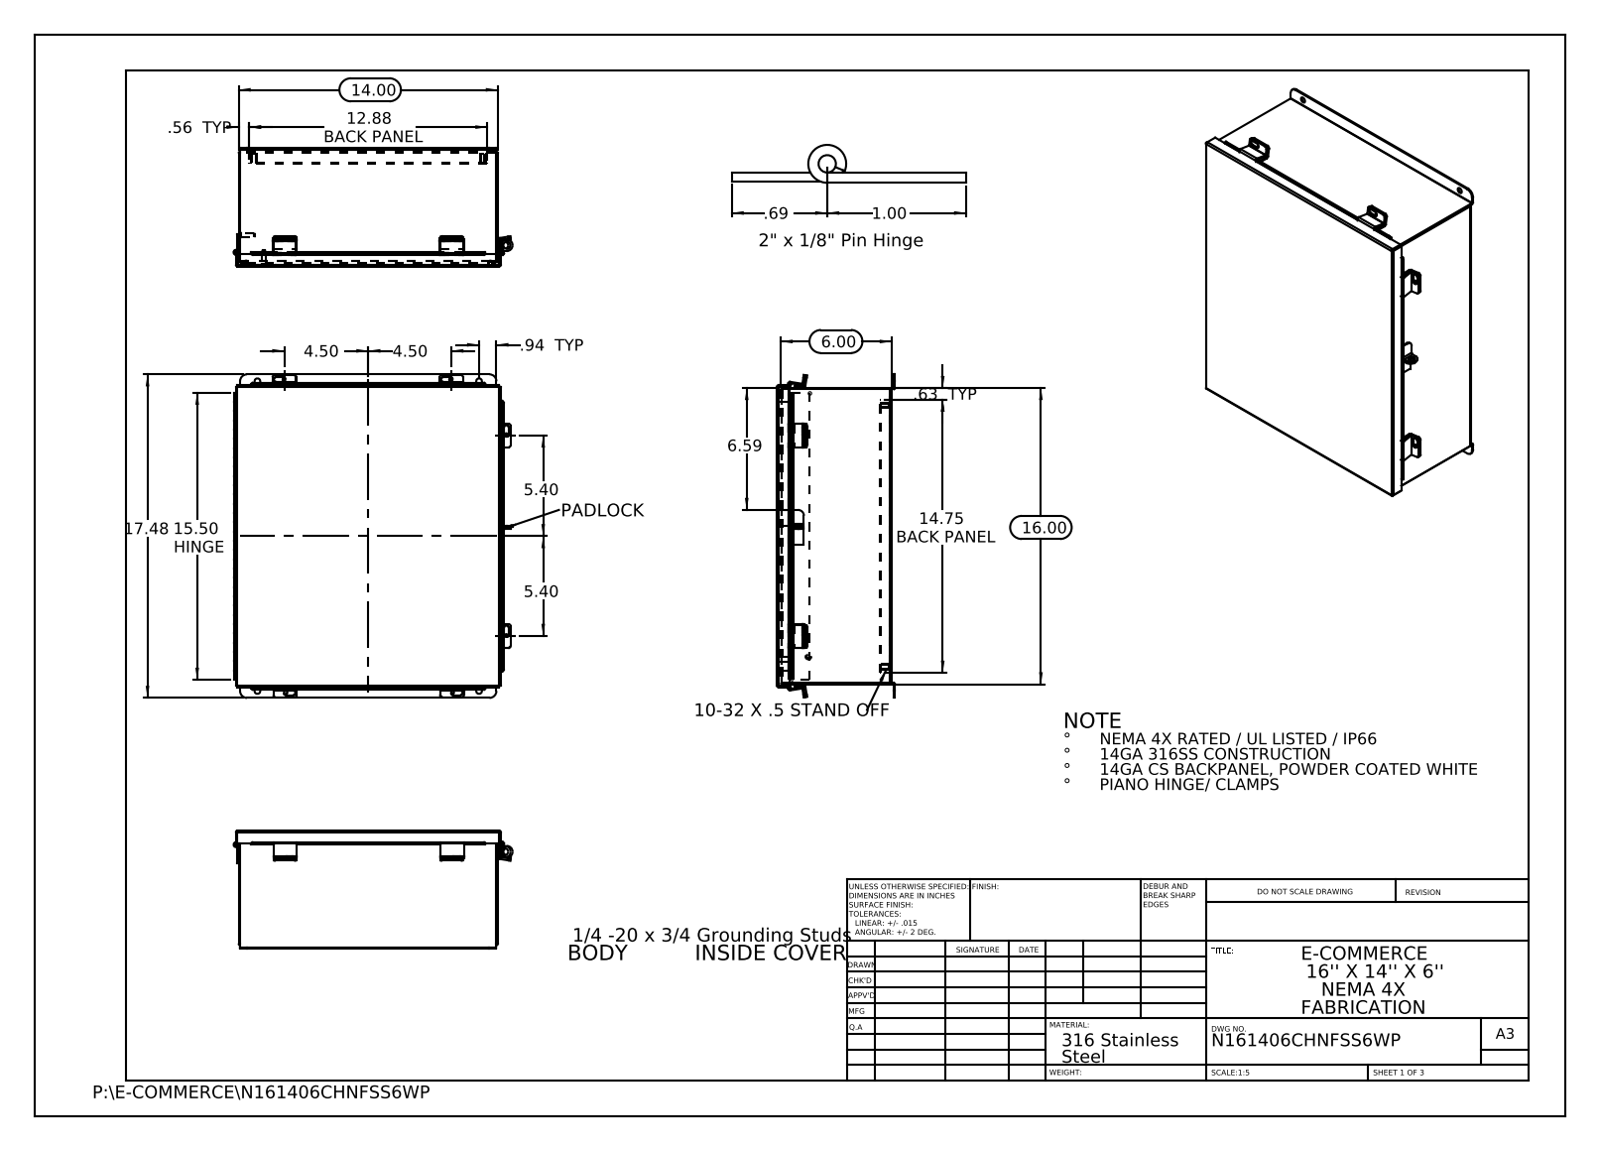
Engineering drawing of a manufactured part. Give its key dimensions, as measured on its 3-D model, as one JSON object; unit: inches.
{"part_name": "N161406CHNFSS6WP Hinge Cover Side JIC; N161406CHNFSS6WP JIC_Cover_Template; HW-CLH-JH-20154; HW-CLH-JH-20104 (+8 more)", "step_written_by": "SolidWorks 2013 (CONFIG_CONTROL_DESIGN)", "units": "inches", "bodies": {"solids": 27, "faces": 866, "planar": 539, "cylindrical": 307, "other": 20}, "overall_size": [17.476, 15.072, 6.39], "volume_in3": 84.84, "surface_area_in2": 2307, "round_holes": [[0.25, 10], [0.187, 4], [0.312, 4], [0.125, 1], [0.125, 1], [0.373, 1], [0.375, 1]], "round_bosses_or_shafts": [[0.313, 4], [0.315, 2], [0.236, 2], [0.273, 1], [0.25, 1]], "partial_cylinders_radius": [[0.125, 21], [0.013, 13], [0.009, 12], [0.088, 12], [0.133, 12], [0.083, 6], [0.1, 6], [0.375, 4]], "face_to_face_distances": [0.075, 6.128, 6.053, 6.203, 0.074, 5.628, 0.575, 0.5, 5.553, 0.649], "hole_center_spacings": [1.315, 12.244, 15.427, 19.652, 9, 11.976, 12.375, 14.126]}
